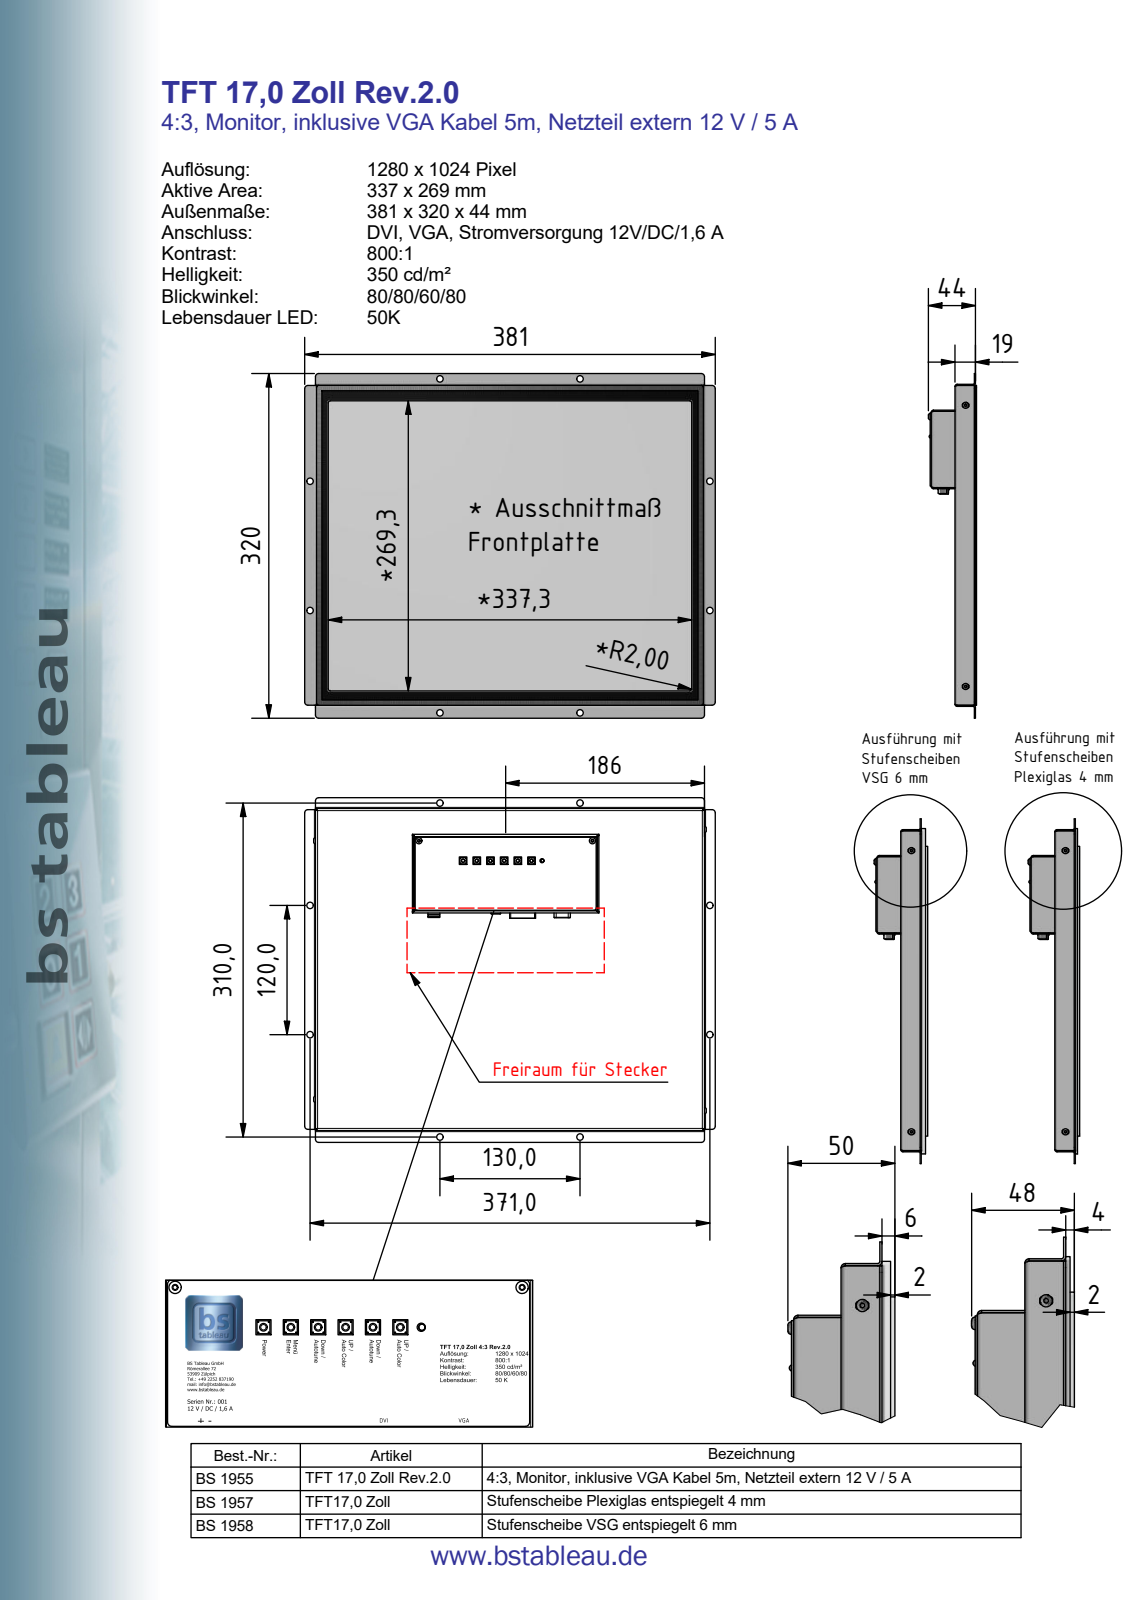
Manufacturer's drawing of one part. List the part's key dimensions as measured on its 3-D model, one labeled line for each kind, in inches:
Part name (STEP PRODUCT): 20000016 TFT 17,0 Zoll 4_3 Rev.2.0; 00000058 TFT17,0 Zoll 4_3 Rev.2.0-UT TDS3160; 00000010 NB-4pol; 00003336 G170EG01 V1 (+8 more)
STEP written by: Autodesk Inventor 2019 (AUTOMOTIVE_DESIGN)
Units: inches
Bodies: 77 solids, 2129 faces (1324 planar, 490 cylindrical, 315 other)
Overall size (bounding box): 15 × 12.598 × 1.758
Volume: 129.2 in³ · Surface area: 941.8 in²
Round holes (diameter × count): ⌀0.097 ×18, ⌀0.031 ×15, ⌀0.213 ×10, ⌀0.236 ×9, ⌀0.126 ×6, ⌀0.134 ×6, ⌀0.098 ×2, ⌀0.173 ×2, ⌀0.15 ×1
Round bosses / shafts (diameter × count): ⌀0.02 ×24, ⌀0.118 ×15, ⌀0.224 ×14, ⌀0.213 ×10, ⌀0.138 ×6, ⌀0.039 ×2, ⌀0.315 ×1, ⌀0.248 ×1
Partial cylindrical surfaces — rounded edges, fillets, slot ends (radius × count): R0.004 ×184, R0.039 ×34, R0.079 ×24, R0.02 ×20, R0.157 ×18, R0.118 ×12, R0.008 ×6, R0.031 ×6
Main face-to-face distances: 0.039, 0.709, 0.748, 0.906, 0.866, 1.614, 0.945, 0.669, 1.575, 0.079
Hole centre spacings: 0.079, 0.07, 0.157, 0.08, 0.125, 0.148, 0.143, 0.197
